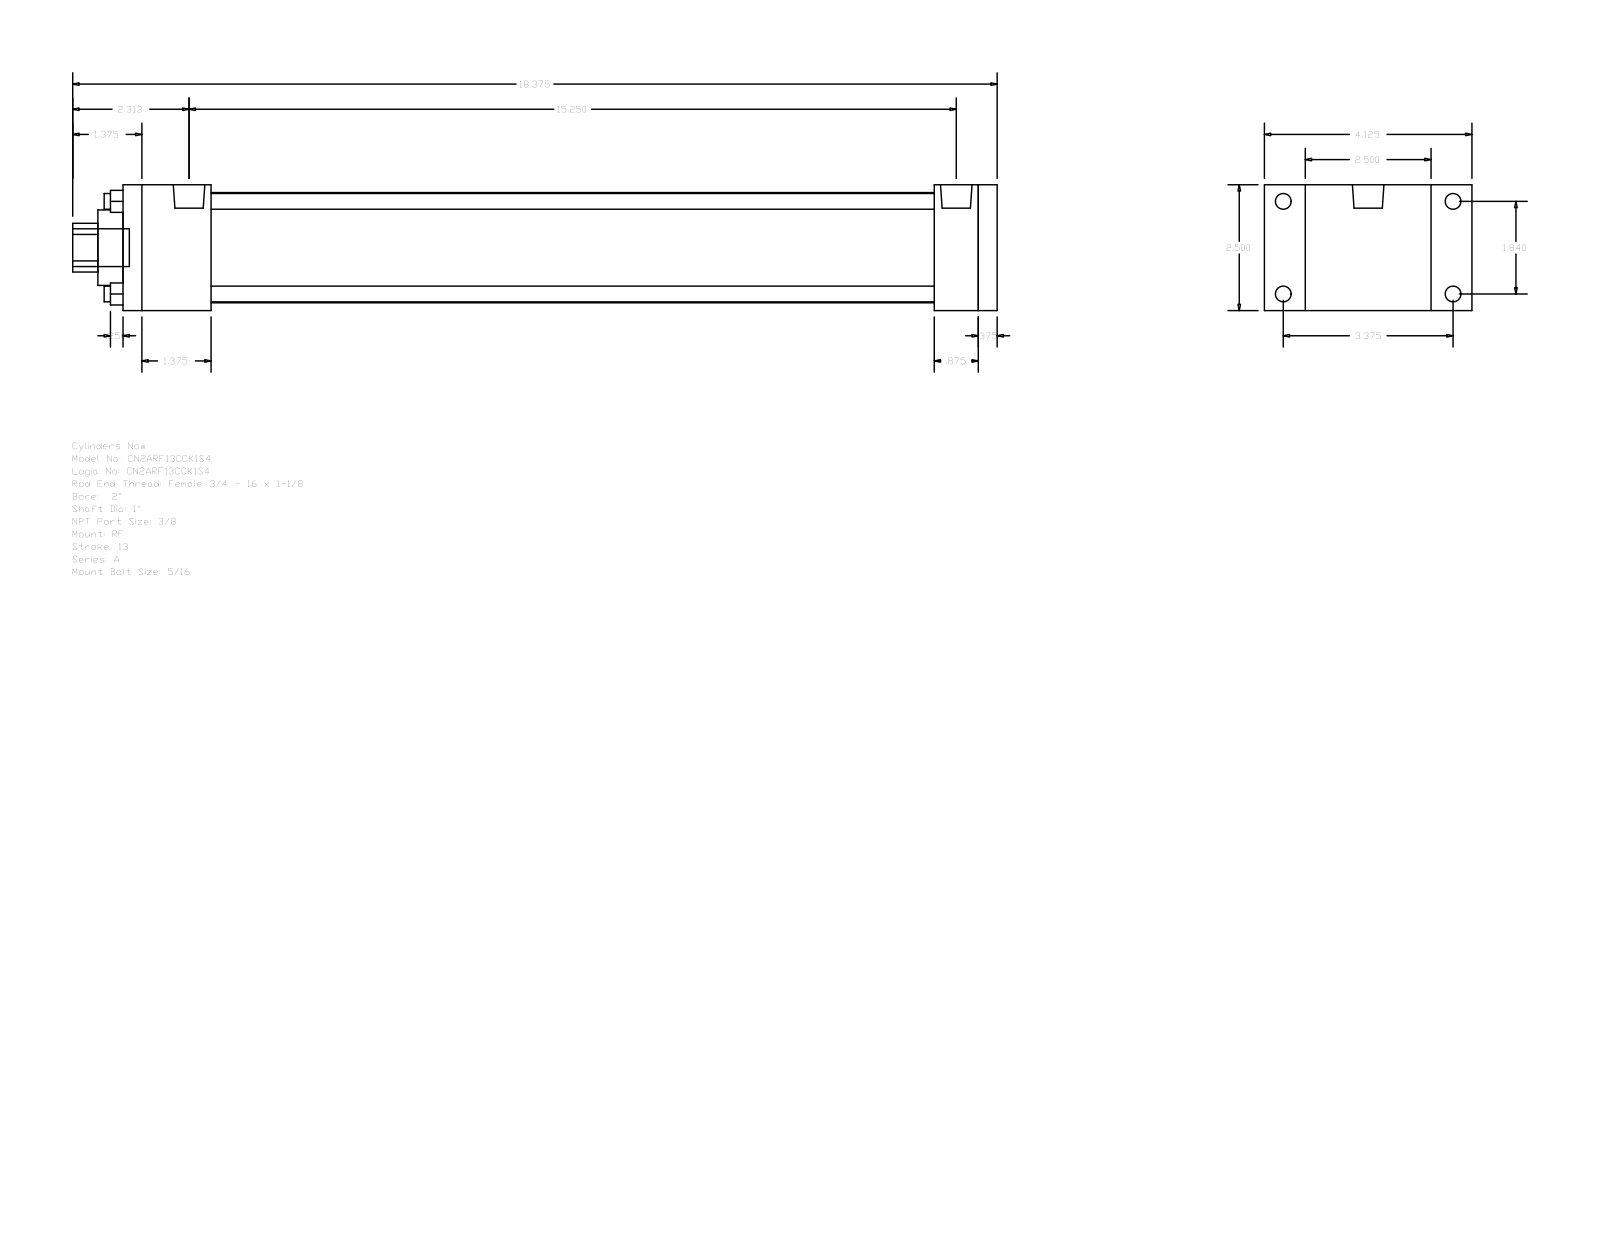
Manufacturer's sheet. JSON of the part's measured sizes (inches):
{"part_name": "A_RF__0200_1", "step_written_by": "GSSL Pune (CONFIG_CONTROL_DESIGN)", "units": "inches", "bodies": {"solids": 0, "faces": 92, "planar": 64, "cylindrical": 28, "other": 0}, "overall_size": [18.375, 4.125, 2.5], "round_holes": [[0.313, 4], [1, 1], [1.5, 1], [2.19, 1]], "round_bosses_or_shafts": [[0.313, 4], [0.219, 4], [0.627, 2], [0.75, 1]], "partial_cylinders_radius": [[0.484, 1]], "face_to_face_distances": [2.5, 0.375, 17.375, 17, 0.813, 1.75, 15.25, 15.625, 16.125, 14.375], "hole_center_spacings": [1.301, 1.84, 2.602]}
